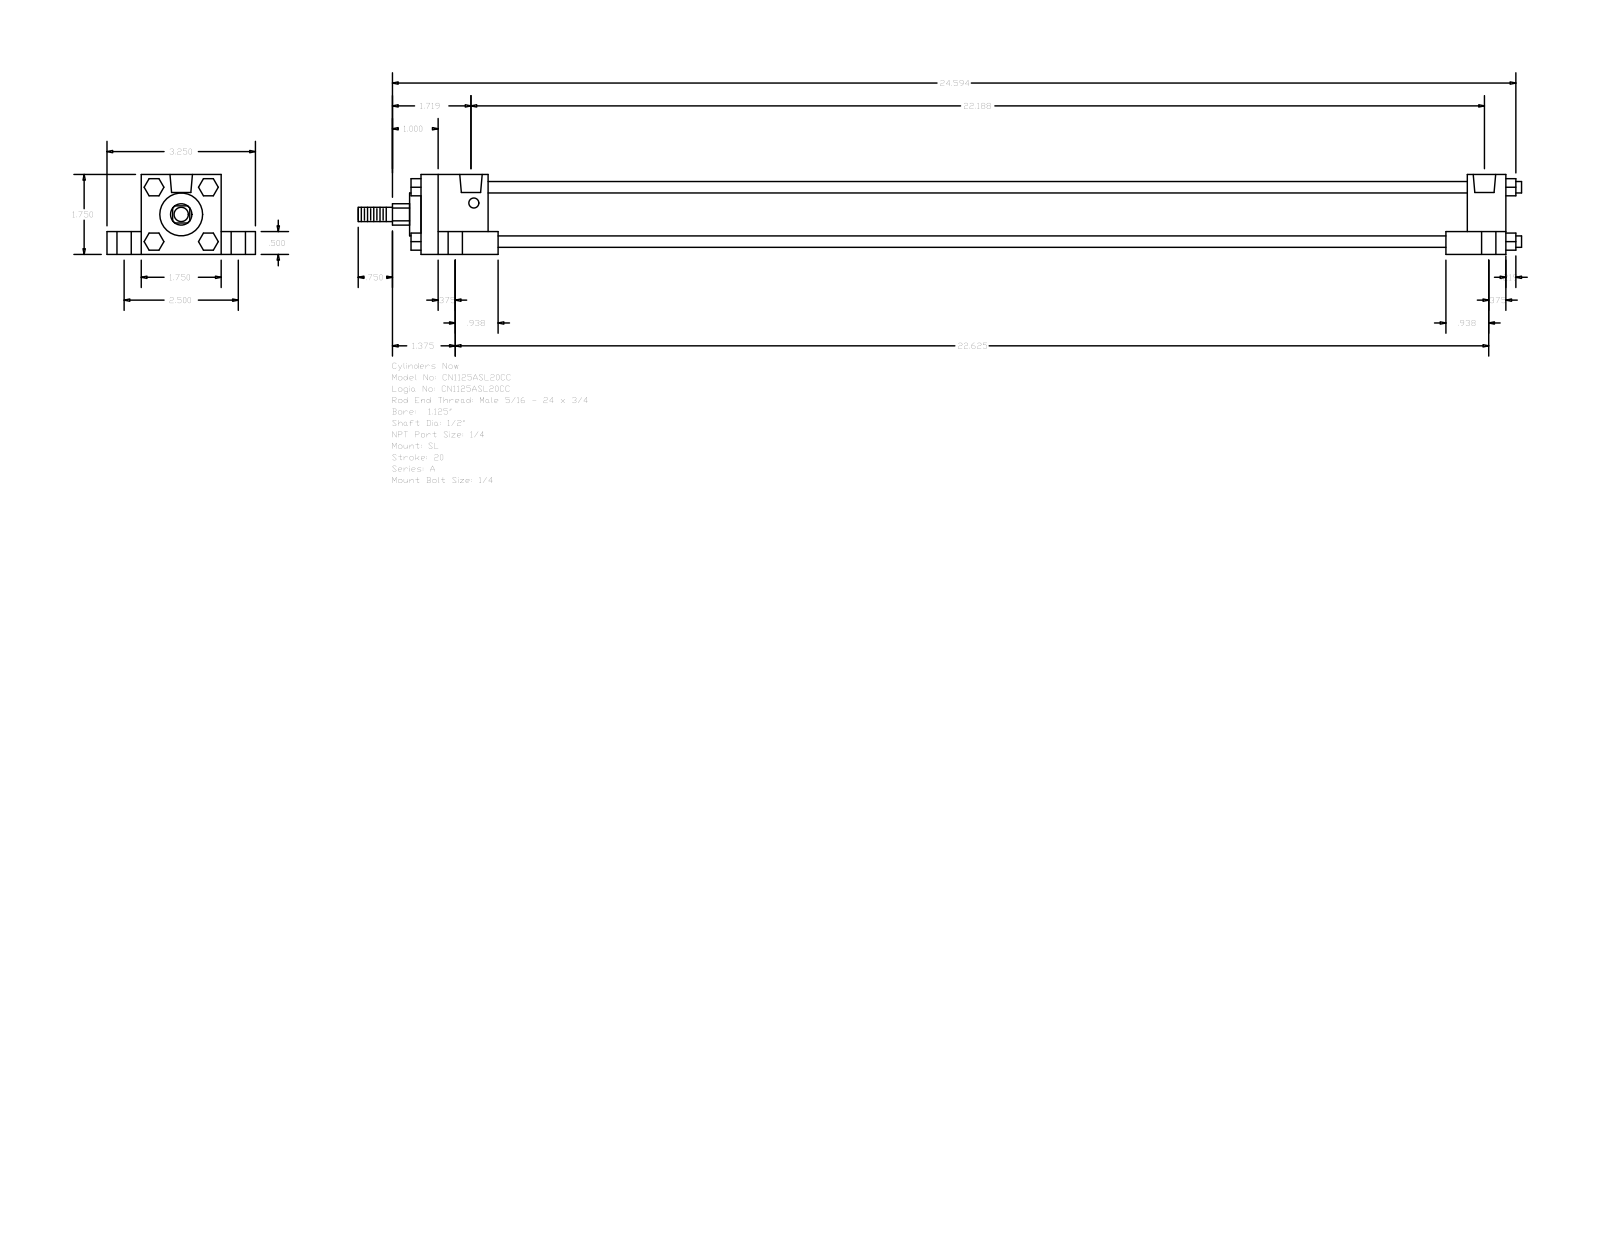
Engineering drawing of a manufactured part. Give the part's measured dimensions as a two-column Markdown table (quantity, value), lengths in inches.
| quantity | value |
| --- | --- |
| part name | A_SL__0112_0.5 |
| STEP written by | GSSL Pune (CONFIG_CONTROL_DESIGN) |
| units | inches |
| bodies | 0 solids, 150 faces (114 planar, 36 cylindrical, 0 other) |
| overall size | 25.469 × 3.25 × 1.75 |
| round holes (diameter × count) | 0.219 × 4, 0.313 × 4, 0.563 × 4, 0.492 × 2 |
| round bosses / shafts (diameter × count) | 0.25 × 4, 1.255 × 1, 0.937 × 1, 0.5 × 1, 0.313 × 1 |
| partial cylindrical surfaces (radius × count) | 0.234 × 1 |
| main face-to-face distances | 1.75, 1.25, 0.5, 0.75, 2.5, 22.281, 23.75, 22.906, 0.844, 1.469 |
| hole center spacings | 1.254, 1.26, 1.296, 1.315, 2.5, 22.063, 22.254, 22.316 |
